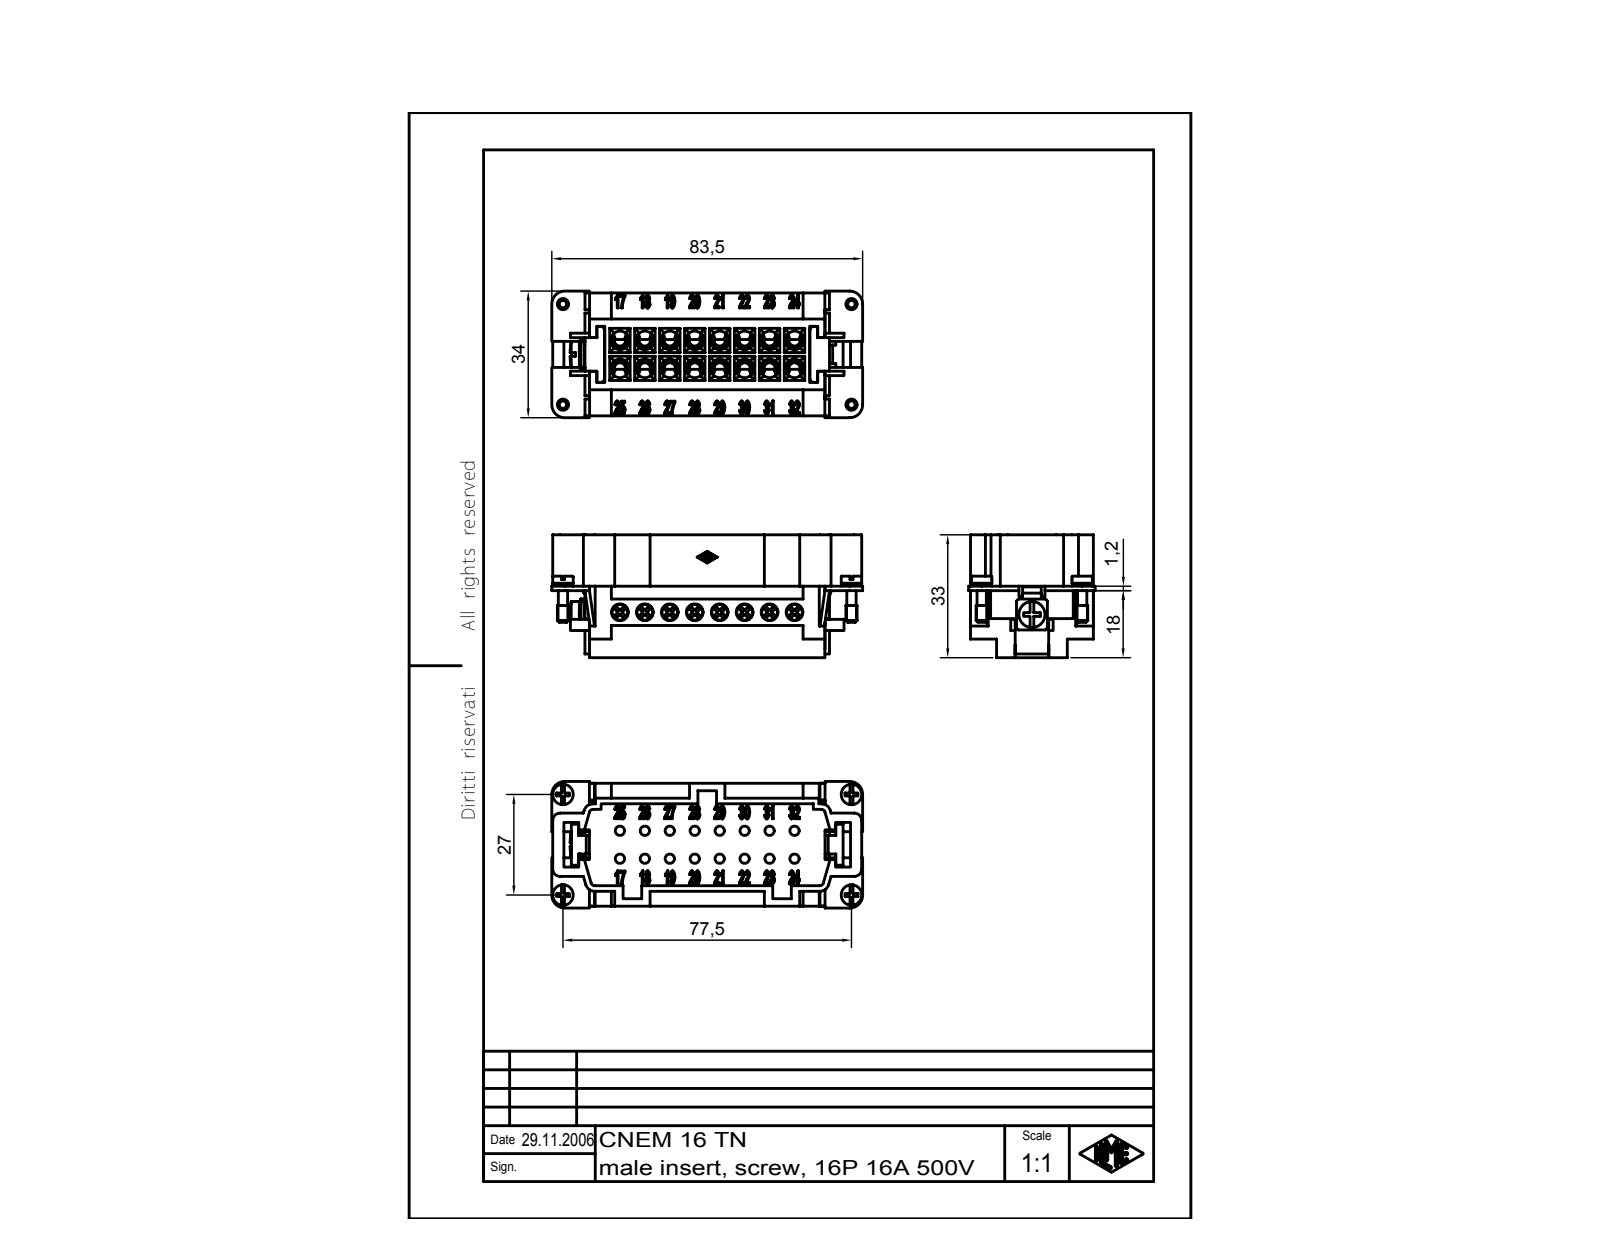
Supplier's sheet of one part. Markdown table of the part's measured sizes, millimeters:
| quantity | value |
| --- | --- |
| part name | CNEM_16_TN |
| STEP written by | PTC Creo Elements/Direct Modeling 19.0E 27-Jun-2016 (C) Parametric Technology GmbH (AUTOMOTIVE_DESIGN) |
| units | millimeters |
| bodies | 1 solid, 1252 faces (813 planar, 293 cylindrical, 146 other) |
| overall size | 84.2 × 34 × 33 |
| volume | 38 424 mm³ |
| surface area | 23 667 mm² |
| round holes (diameter × count) | 5 × 24, 3 × 4, 2.58 × 1, 4 × 1 |
| round bosses / shafts (diameter × count) | 2.5 × 16, 6 × 5, 5.5 × 4, 2.3 × 4, 7 × 1 |
| partial cylindrical surfaces (radius × count) | 1.3 × 18, 1.6 × 16, 1 × 11, 2 × 10, 3.8 × 8, 0.5 × 6, 1.5 × 4, 3.5 × 4 |
| main face-to-face distances | 1.2, 20.2, 2, 1.8, 3.5, 0.5, 19, 3.25, 18.4, 21.4 |
| hole center spacings | 6.7, 13.4, 20.1, 10.06, 15.36, 26.8, 21.45, 33.5 |
